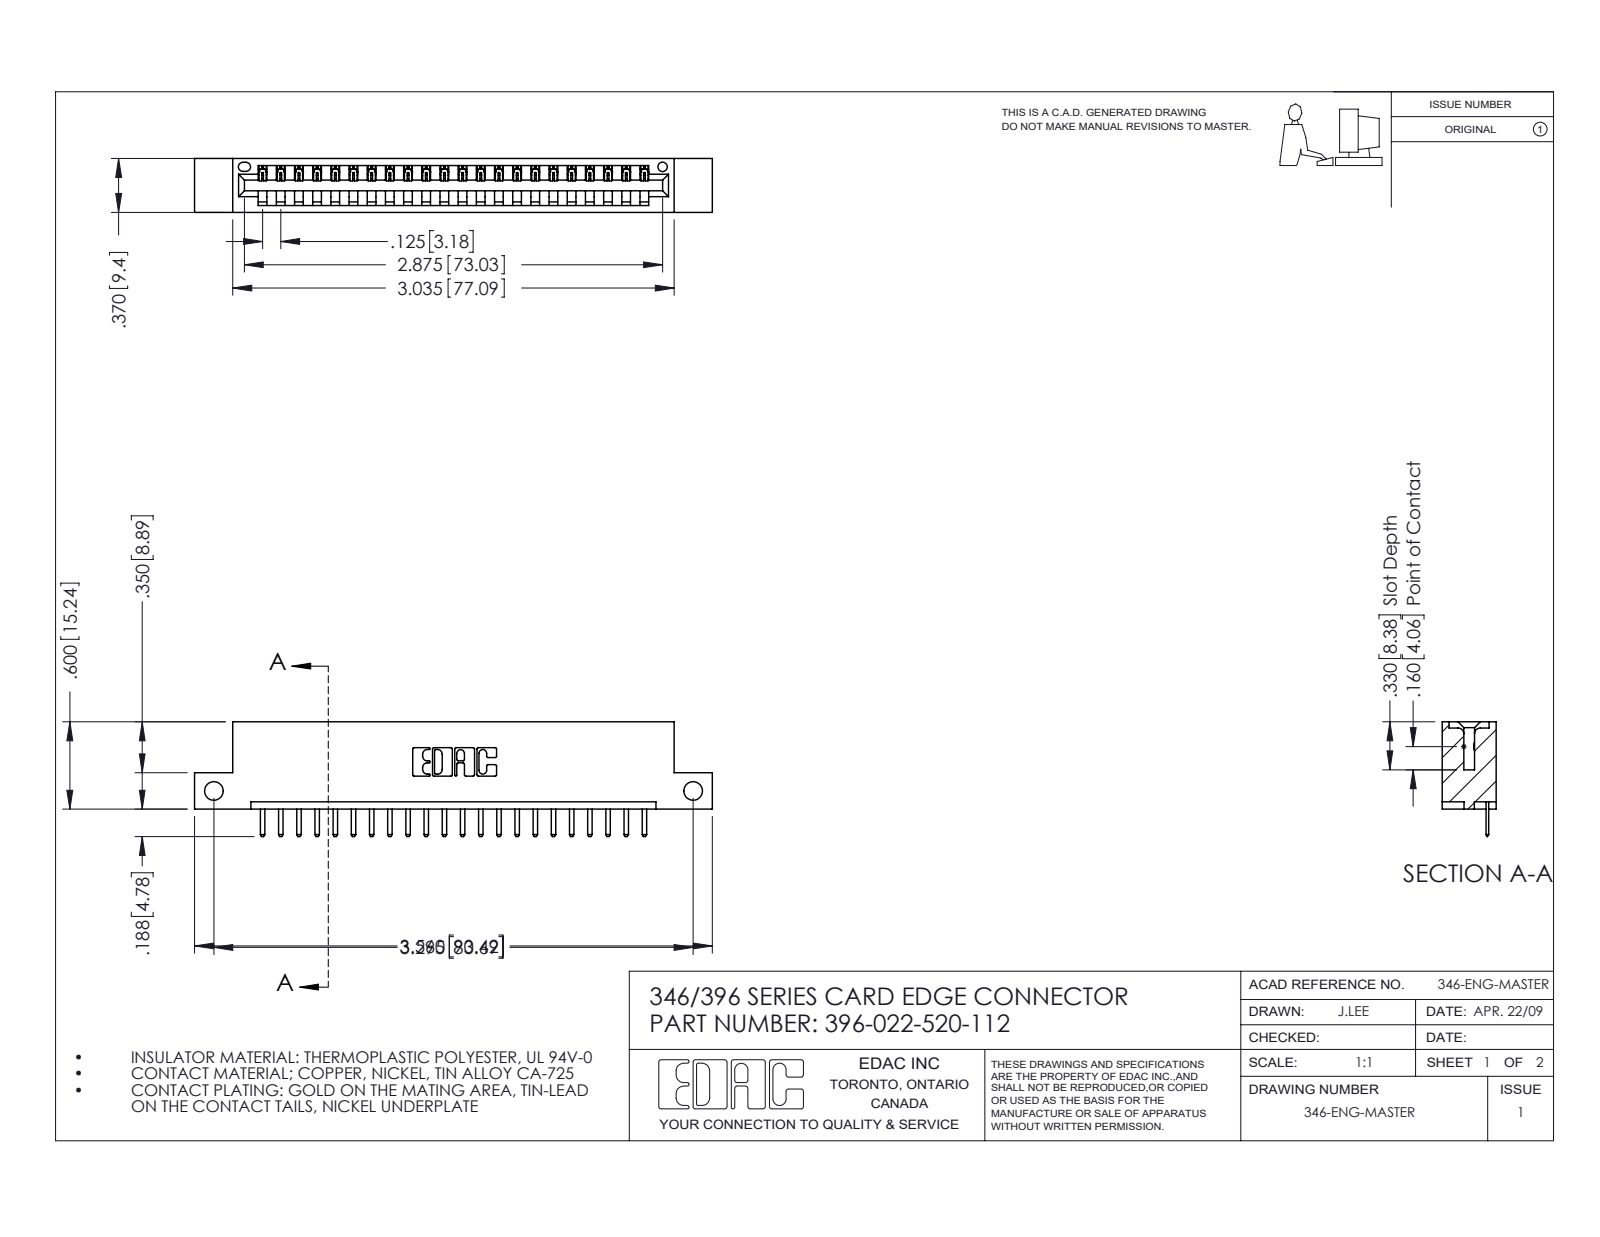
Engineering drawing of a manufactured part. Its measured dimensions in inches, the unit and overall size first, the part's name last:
Units: inches
Overall size (bounding box): 3.56 × 0.788 × 0.37
Round holes (diameter × count): ⌀0.128 ×2, ⌀0.064 ×1
Partial cylindrical surfaces — rounded edges, fillets, slot ends (radius × count): R0.01 ×46, R0.006 ×44, R0.01 ×22, R0.007 ×6, R0.031 ×6, R0.026 ×3, R0.031 ×2, R0.04 ×2
Main face-to-face distances: 0.048, 0.322, 0.37, 0.25, 0.148, 0.222, 0.1, 0.174, 0.072, 0.298
Hole centre spacings: 3.295
Volume: 0.511 in³ · Surface area: 15.32 in²
Bodies: 23 solids, 1486 faces (1000 planar, 486 cylindrical, 0 other)
Part name (STEP PRODUCT): 346 Part_Flush Mounting Lugs - Side Mount; 345-292-001_345-293-120; 396-022-520-112
STEP written by: SolidWorks 2016 (CONFIG_CONTROL_DESIGN)
